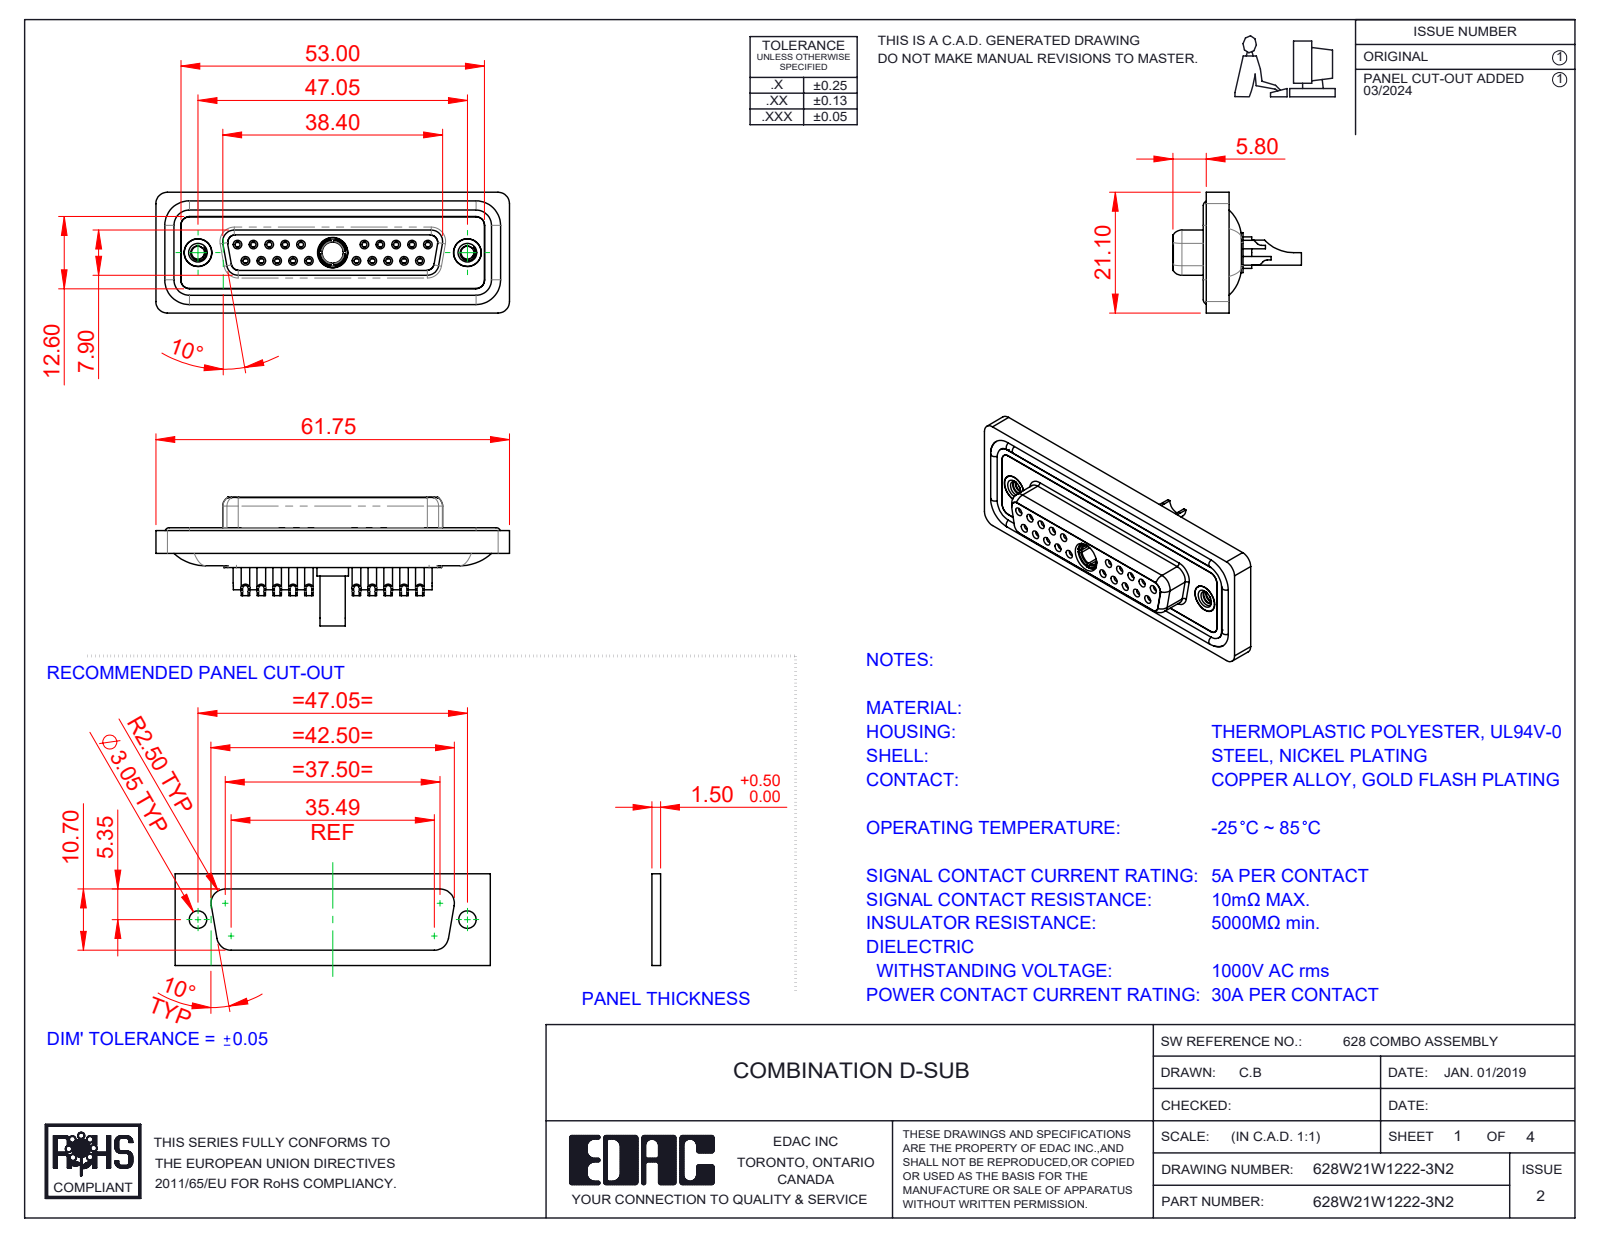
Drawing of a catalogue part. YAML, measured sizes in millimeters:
part_name: "628Combo Shell Rear_25 Contacts; 628Combo Threaded Rivet_2; 628Combo Housing_21W1; Power Socket_30A SC (+5 more)"
step_written_by: "SolidWorks 2023 (CONFIG_CONTROL_DESIGN)"
units: millimeters
bodies: {solids: 29, faces: 1566, planar: 477, cylindrical: 634, other: 455}
overall_size: [61.75, 22.45, 21.1]
volume: 8439
surface_area: 14320
round_holes:
  - {diameter: 0.9, count: 20}
  - {diameter: 1, count: 20}
  - {diameter: 1.1, count: 20}
  - {diameter: 1.5, count: 20}
  - {diameter: 2, count: 20}
  - {diameter: 1.6, count: 10}
  - {diameter: 1.7, count: 10}
  - {diameter: 4.85, count: 3}
  - {diameter: 2.26, count: 2}
  - {diameter: 4, count: 2}
  - {diameter: 4.05, count: 2}
  - {diameter: 5, count: 2}
round_bosses_or_shafts:
  - {diameter: 2.2, count: 20}
  - {diameter: 1.6, count: 14}
  - {diameter: 4.95, count: 2}
  - {diameter: 4.8, count: 2}
  - {diameter: 5.5, count: 1}
  - {diameter: 5.2, count: 1}
  - {diameter: 4.96, count: 1}
  - {diameter: 4.75, count: 1}
partial_cylinders:
  - {radius: 1.5, count: 22}
  - {radius: 2, count: 18}
  - {radius: 1.35, count: 8}
  - {radius: 1.6, count: 8}
  - {radius: 1, count: 6}
  - {radius: 0.25, count: 4}
  - {radius: 0.5, count: 4}
  - {radius: 0.6, count: 4}
face_to_face_distances: [0.4, 1.8, 7.45, 5.65, 6.6, 0.5, 1.6, 7.05, 2.9, 1.1]
hole_center_spacings: [3.16, 2.77, 5.54, 5.03, 8.31, 7.48, 16.62, 19.39]
